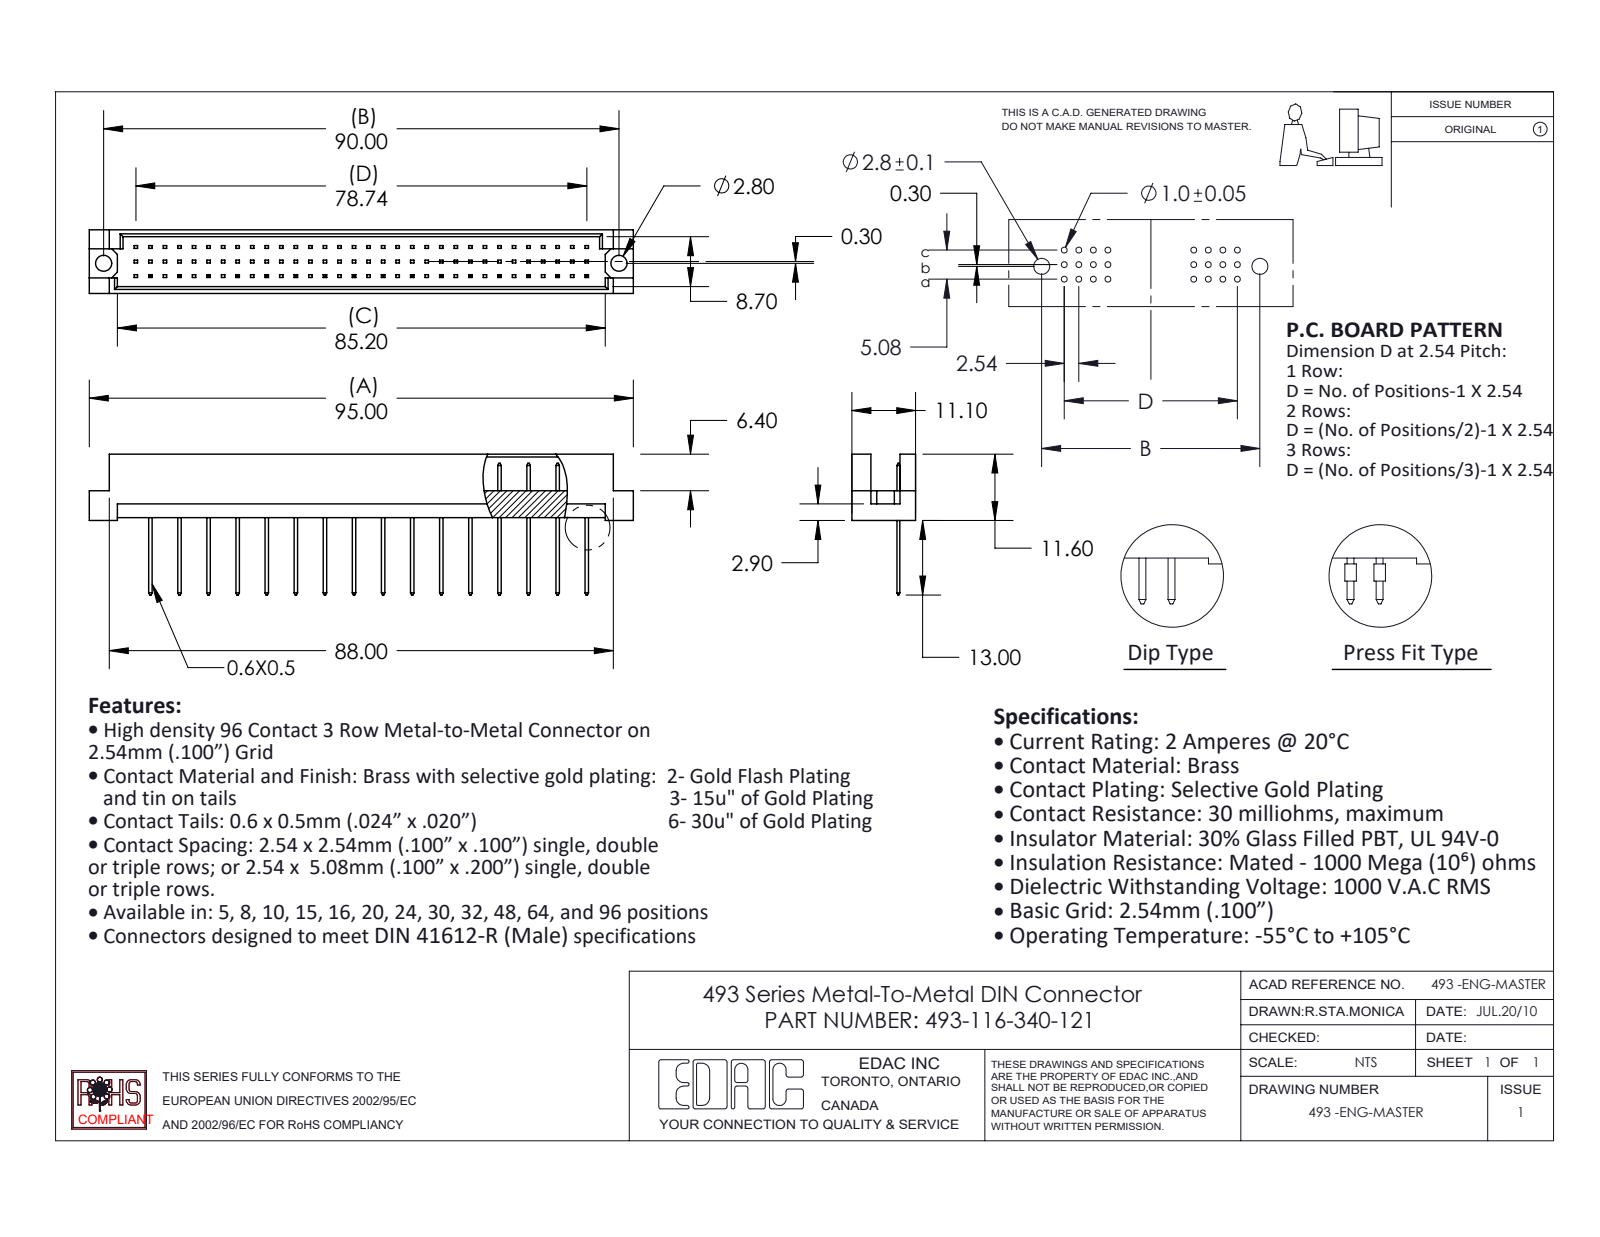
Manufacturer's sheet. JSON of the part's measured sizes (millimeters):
{"part_name": "493-116-340-121; 493-290_40; 493 Part_96", "step_written_by": "SolidWorks 2020 (CONFIG_CONTROL_DESIGN)", "units": "millimeters", "bodies": {"solids": 17, "faces": 660, "planar": 656, "cylindrical": 4, "other": 0}, "overall_size": [95, 24.6, 11.1], "volume_mm3": 5768, "surface_area_mm2": 7278, "round_holes": [[2.8, 2]], "face_to_face_distances": [1.2, 9.9, 11.1, 8.7, 4.7, 0.5, 5.08, 2.76, 3.26, 7.84], "hole_center_spacings": [90]}
